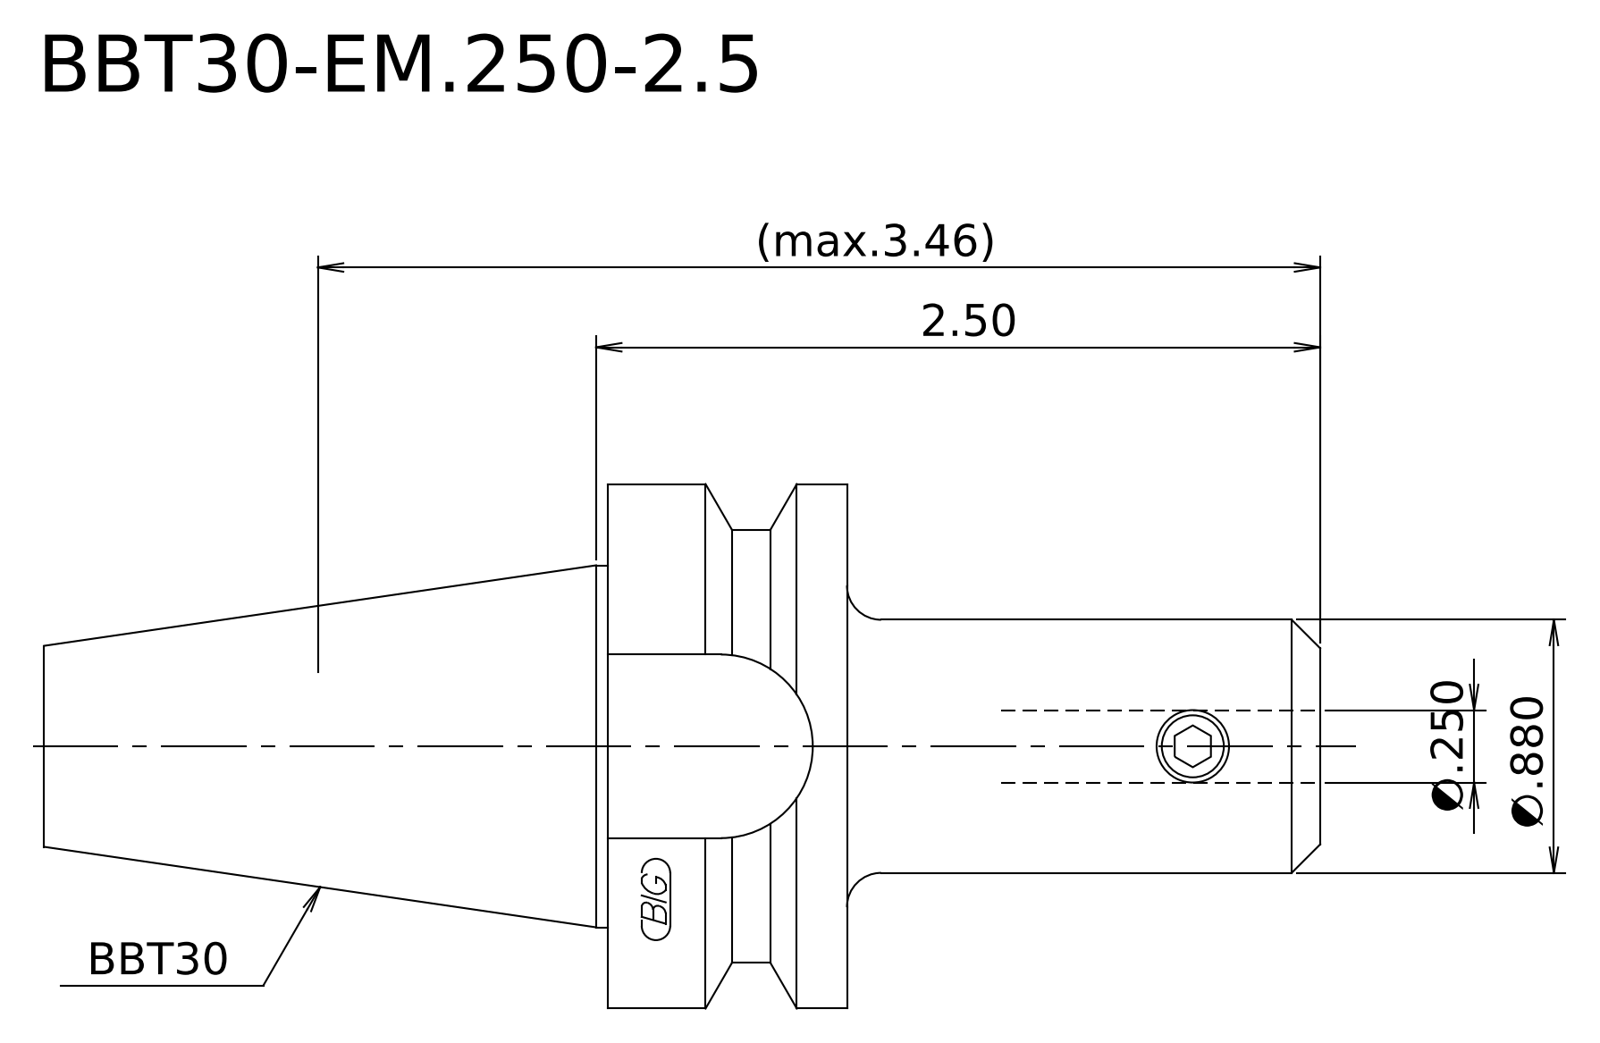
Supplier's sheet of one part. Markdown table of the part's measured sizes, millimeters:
| quantity | value |
| --- | --- |
| part name | BBT30-EM_250-2_5 |
| STEP written by | SolidWorks 2021 (CONFIG_CONTROL_DESIGN) |
| units | millimeters |
| bodies | 1 solid, 27 faces (7 planar, 12 cylindrical, 8 other) |
| overall size | 111.9 × 46 × 46 |
| volume | 69 873 mm³ |
| surface area | 13 803 mm² |
| round holes (diameter × count) | 6.35 × 1 |
| round bosses / shafts (diameter × count) | 46 × 1, 38 × 1, 31.75 × 1, 22.22 × 1 |
| main face-to-face distances | 20.5, 69.4, 48.9, 42.5, 63, 111.9, 47.4, 50.4, 4.9, 7.9 |
